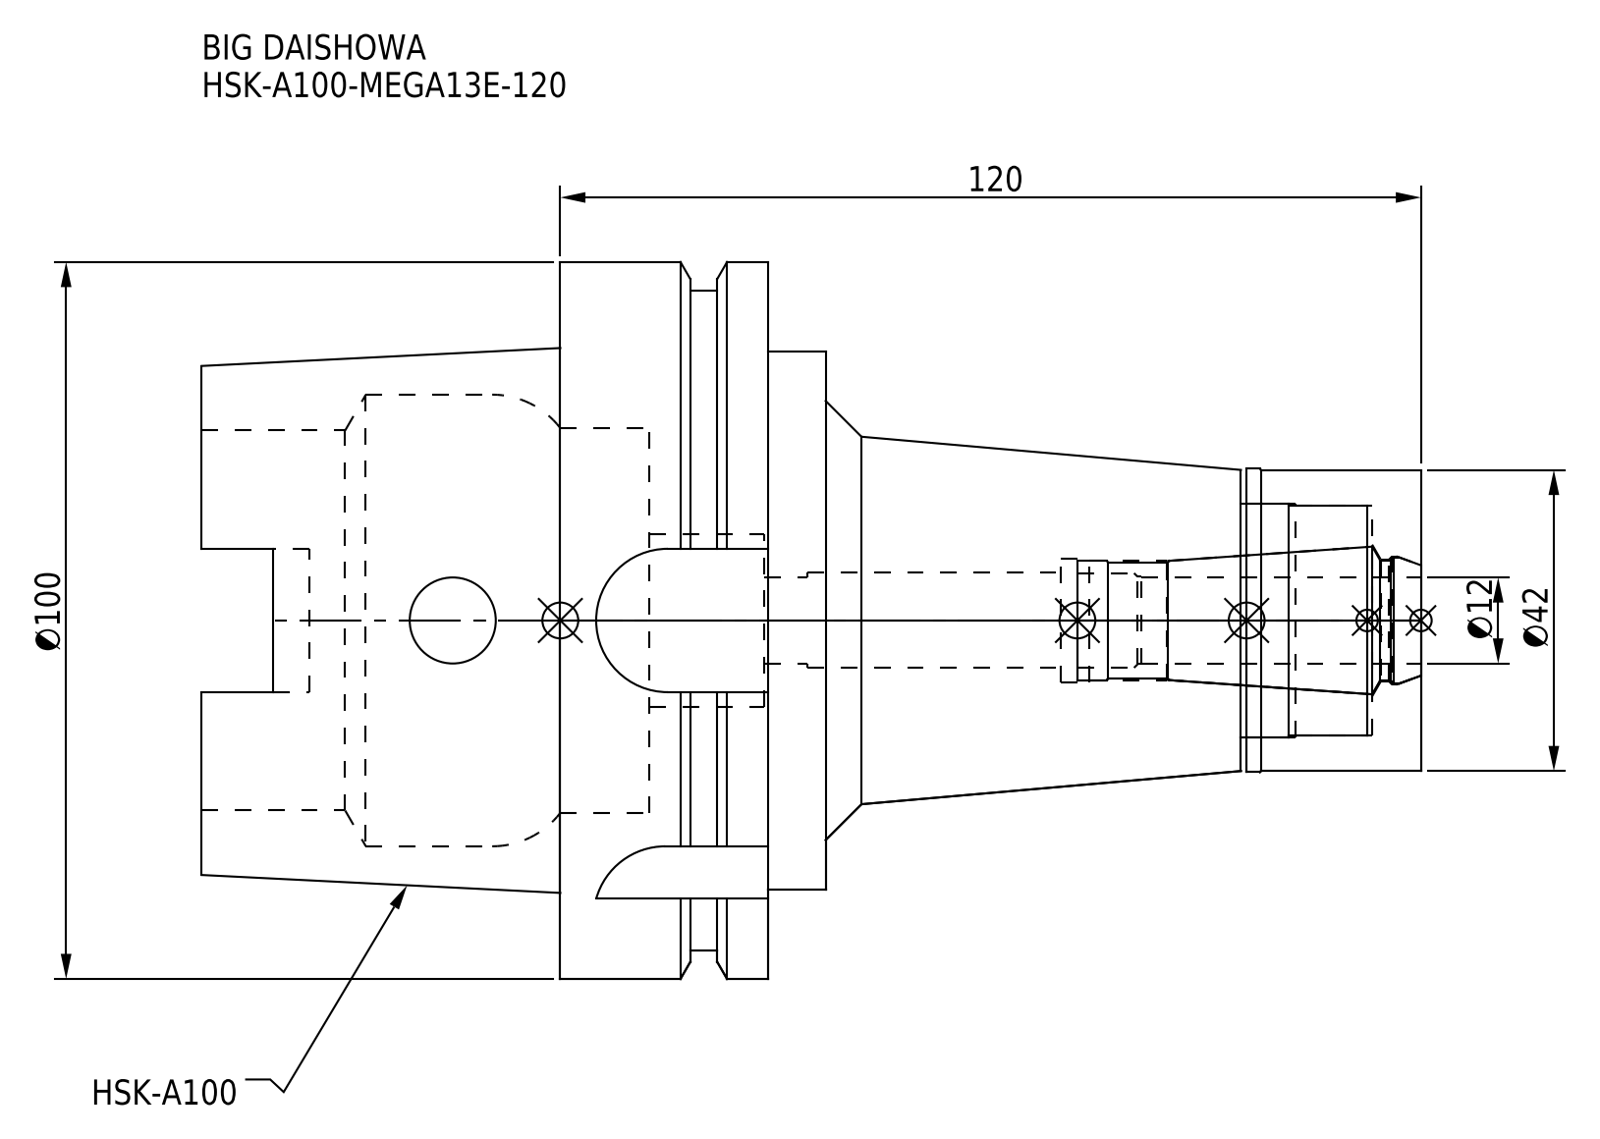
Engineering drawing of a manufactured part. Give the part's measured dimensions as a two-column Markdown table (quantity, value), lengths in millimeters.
| quantity | value |
| --- | --- |
| part name | HSK-A100-MEGA13E-120-120.stp; MEN13_1.stp; HA100ME13120-120_ASM.stp; HSK-A100-MEGA13E-120 (+3 more) |
| STEP written by | SolidWorks 2019 (CONFIG_CONTROL_DESIGN) |
| units | millimeters |
| bodies | 2 solids, 126 faces (42 planar, 56 cylindrical, 28 other) |
| overall size | 170 × 100 × 100 |
| volume | 407 842 mm³ |
| surface area | 72 640 mm² |
| round holes (diameter × count) | 12 × 2, 13.3 × 1, 16.6 × 1, 17 × 1, 17.2 × 1, 17.9 × 1, 24 × 1, 32 × 1, 32.5 × 1, 53 × 1, 53.8 × 1, 63 × 1 |
| round bosses / shafts (diameter × count) | 100 × 1, 92 × 1, 75 × 1, 42.3 × 1, 42 × 1 |
| partial cylindrical surfaces (radius × count) | 4.88 × 4, 10 × 4 |
| main face-to-face distances | 29, 16.55, 12.45, 8, 24.55, 37, 83, 91, 107.55, 120 |
